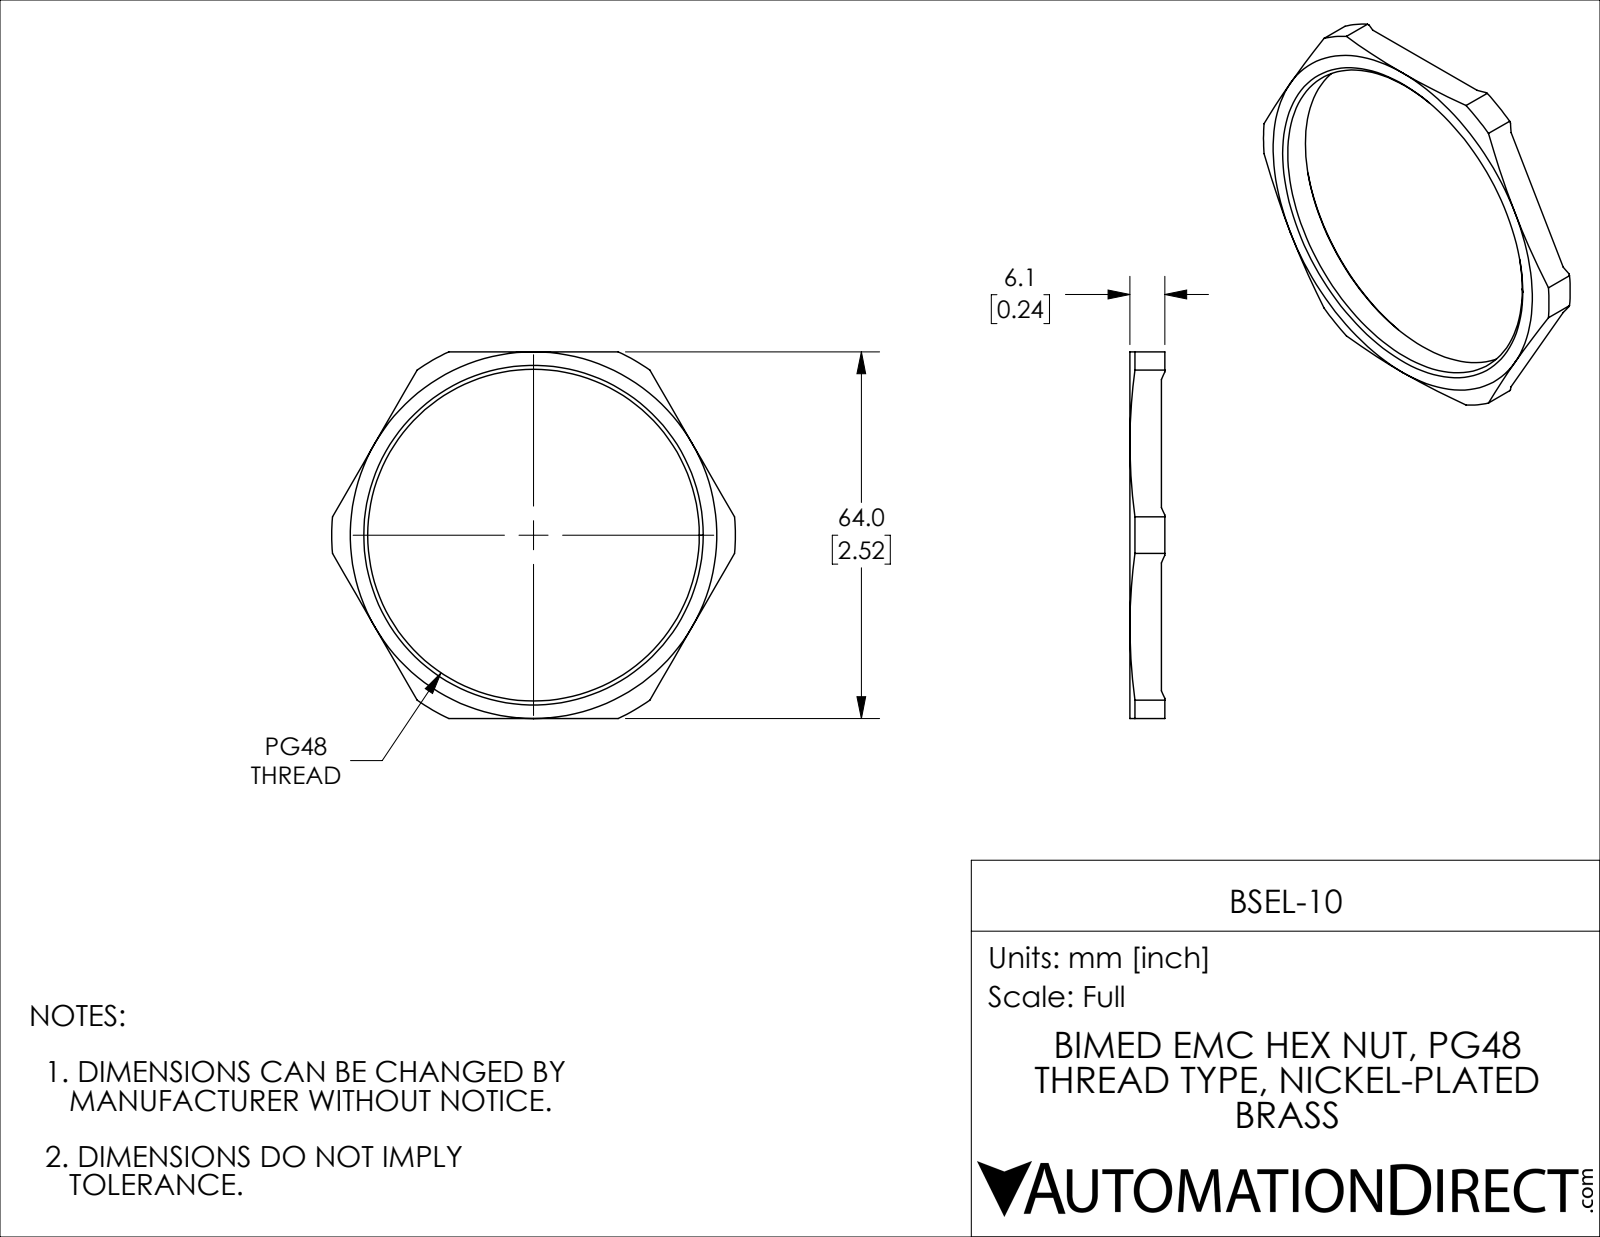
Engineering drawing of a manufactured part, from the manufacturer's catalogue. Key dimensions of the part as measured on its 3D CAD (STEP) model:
Part name (STEP PRODUCT): BSEL-10
STEP written by: SolidWorks 2021 (CONFIG_CONTROL_DESIGN)
Units: millimetres
Bodies: 1 solid, 46 faces (14 planar, 8 cylindrical, 24 other)
Overall size (bounding box): 70.5 × 64 × 6.1
Volume: 4 693 mm³ · Surface area: 3 788 mm²
Round holes (diameter × count): ⌀57.9 ×1
Partial cylindrical surfaces — rounded edges, fillets, slot ends (radius × count): R35.25 ×1
Main face-to-face distances: 64, 5.5, 0.6, 6.1
